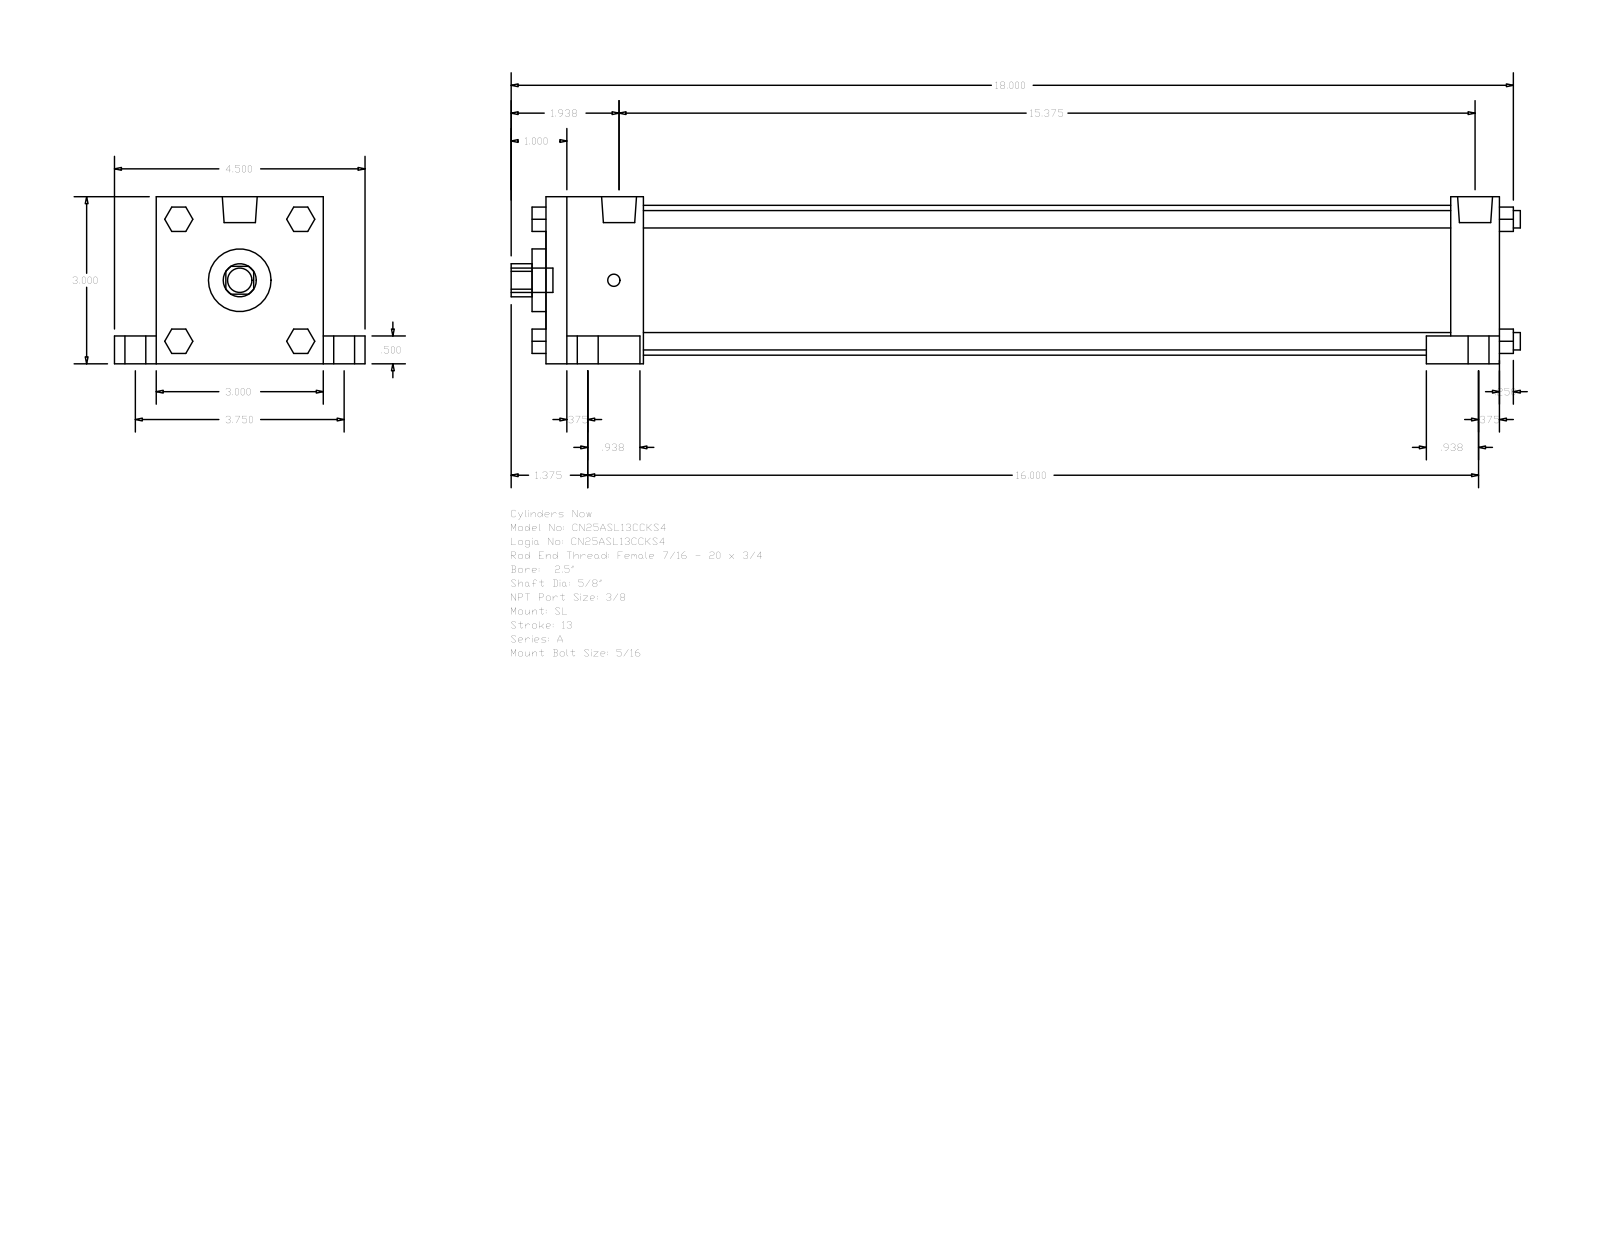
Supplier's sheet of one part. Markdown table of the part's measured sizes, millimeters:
| quantity | value |
| --- | --- |
| part name | A_SL__0250_0.625 |
| STEP written by | GSSL Pune (CONFIG_CONTROL_DESIGN) |
| units | millimeters |
| bodies | 0 solids, 148 faces (112 planar, 36 cylindrical, 0 other) |
| overall size | 460.38 × 114.3 × 76.2 |
| round holes (diameter × count) | 15.88 × 1, 28.57 × 1, 68.33 × 1 |
| round bosses / shafts (diameter × count) | 15.88 × 4, 9.53 × 4, 7.94 × 4, 5.56 × 4, 15.93 × 2, 11.11 × 1 |
| partial cylindrical surfaces (radius × count) | 7.54 × 1 |
| main face-to-face distances | 76.2, 434.97, 44.45, 390.52, 412.74, 368.29, 22.23, 12.7, 63.5, 19.05 |
